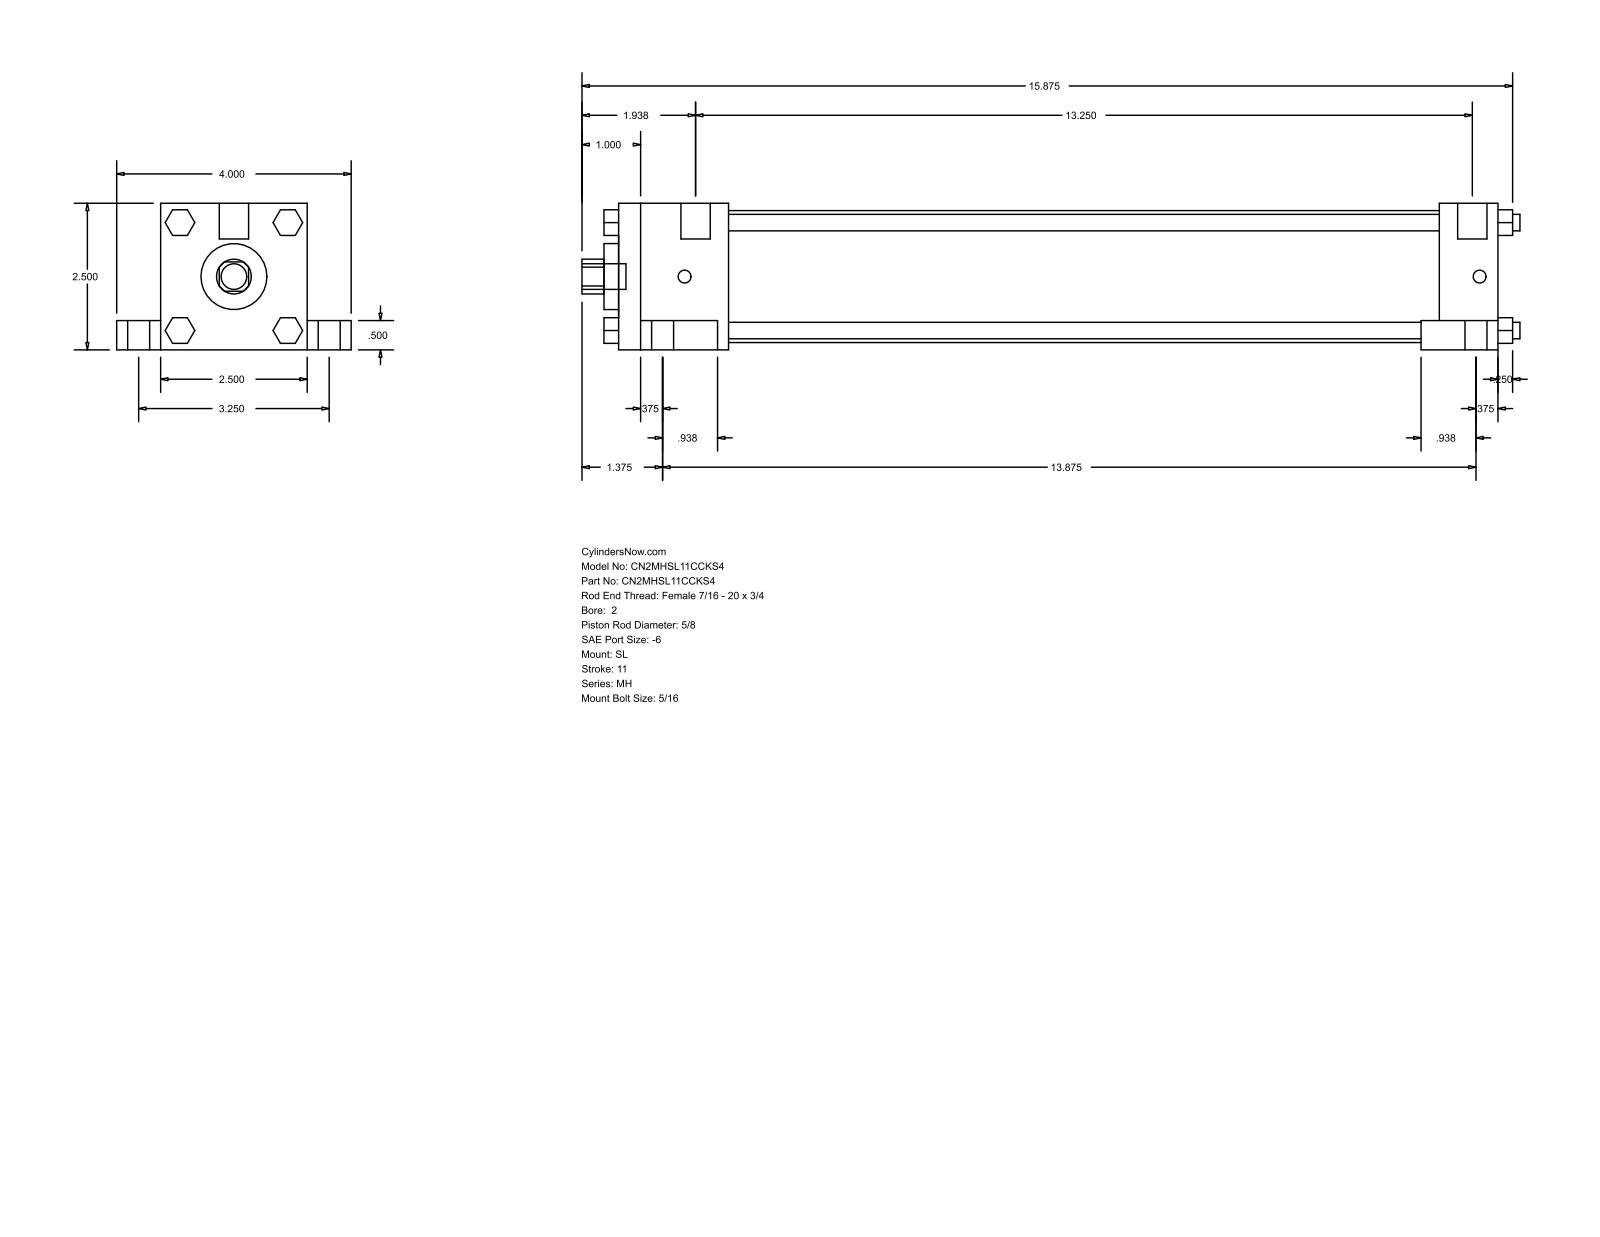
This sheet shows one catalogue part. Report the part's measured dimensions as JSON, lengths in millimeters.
{"part_name": "MH_SL__0200_0.625", "step_written_by": "GSSL Pune (CONFIG_CONTROL_DESIGN)", "units": "millimeters", "bodies": {"solids": 0, "faces": 148, "planar": 112, "cylindrical": 36, "other": 0}, "overall_size": [406.4, 101.6, 63.5], "round_holes": [[15.88, 1], [28.57, 1], [57.15, 1]], "round_bosses_or_shafts": [[15.88, 4], [9.53, 4], [7.14, 4], [5.56, 4], [12.7, 2], [11.11, 1]], "partial_cylinders_radius": [[7.54, 1]], "face_to_face_distances": [63.5, 381, 12.7, 19.05, 50.8, 82.55, 25.4, 355.6, 47.62, 307.98]}
